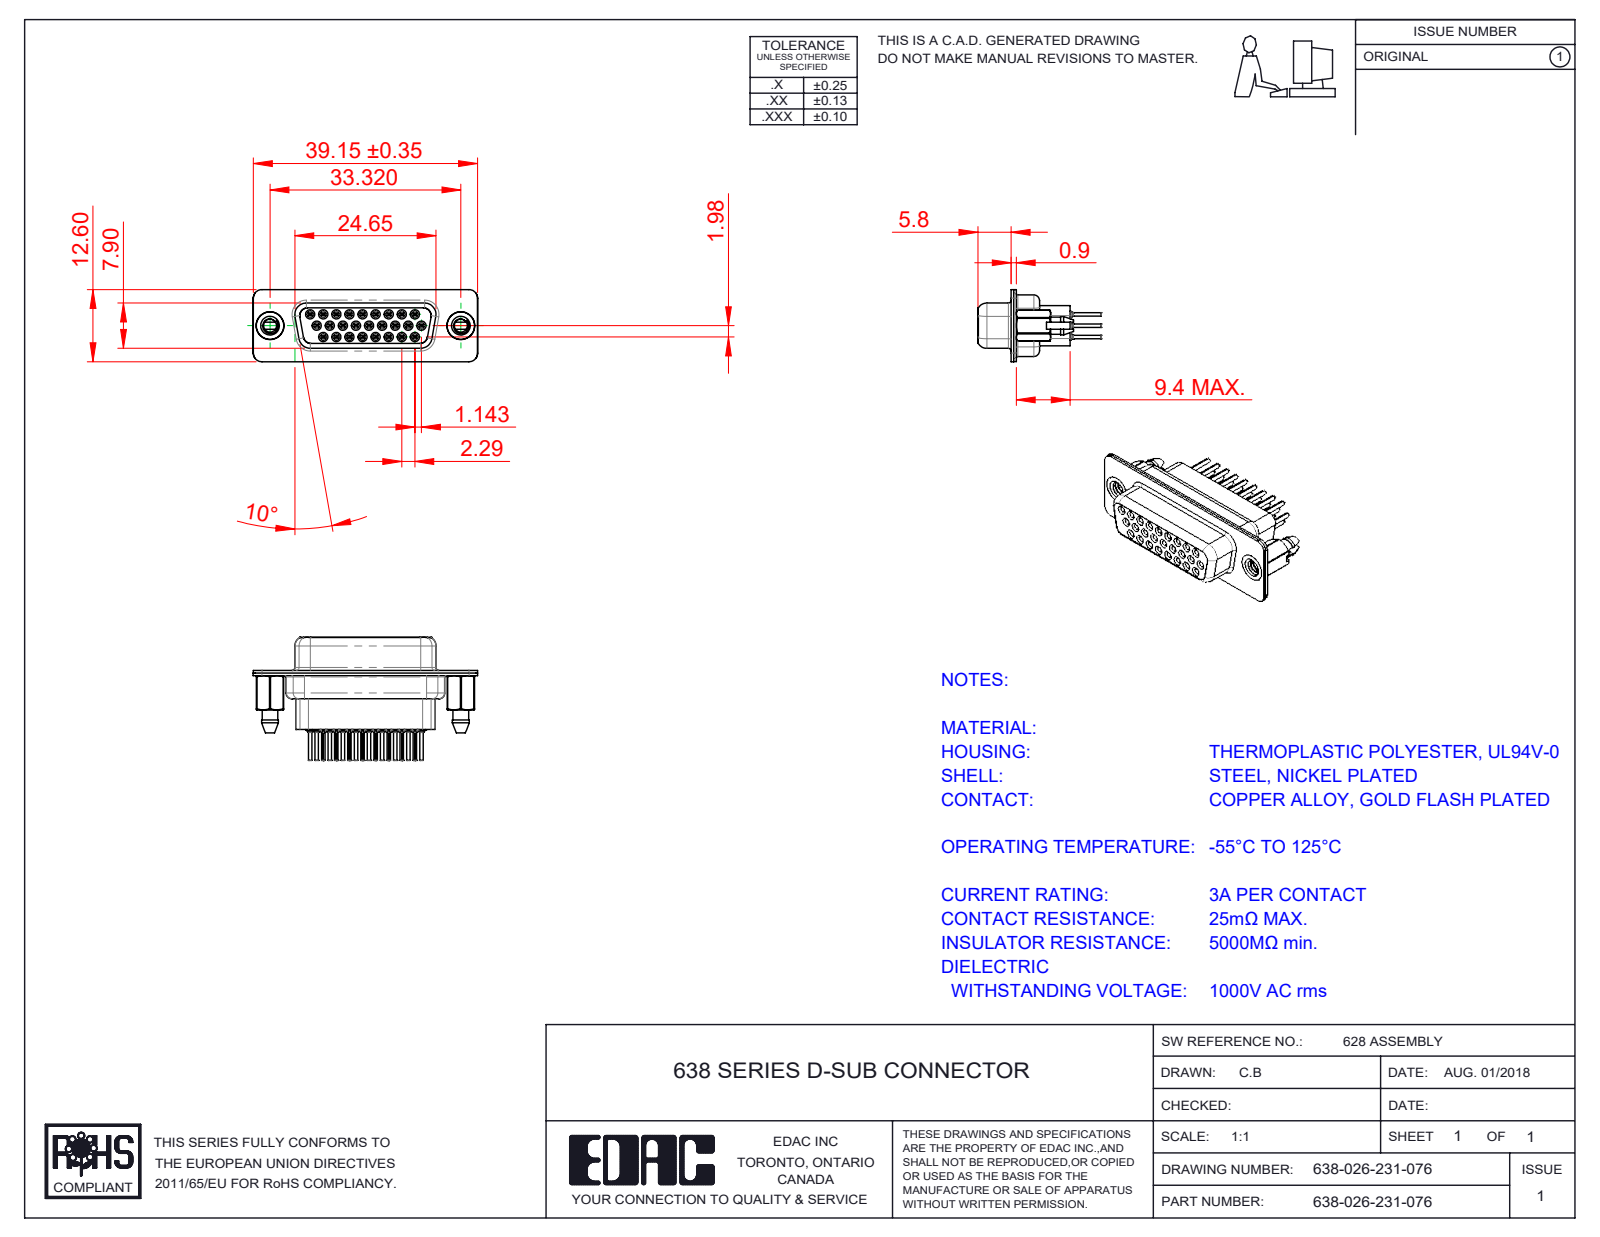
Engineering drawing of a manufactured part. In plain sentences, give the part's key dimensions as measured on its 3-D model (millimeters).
The part is named "638 4-40 Threaded Boardlock_LP; 638 Housing_26 Contacts HP; 638-026-231-076; 638 Shell Front_26 Contacts (+4 more)". Its 3-D file was written by "SolidWorks 2020 (CONFIG_CONTROL_DESIGN)". It is 31 solids with 3551 faces: 905 planar, 1027 cylindrical and 1619 other. Overall it measures 39.19 by 21.5 by 12.6 millimeters. Its volume is 2 790 cubic millimeters and its surface area 10 158 square millimeters. Round holes: 26 of diameter 0.2, 26 of diameter 0.8, 26 of diameter 1, 26 of diameter 1.1, 26 of diameter 1.6, 26 of diameter 1.7, 26 of diameter 1.8, 2 of diameter 2.26, 2 of diameter 4, 2 of diameter 4.05, 2 of diameter 4.85. Round bosses or shafts: 26 of diameter 2, 26 of diameter 1.5, 26 of diameter 1.2, 26 of diameter 0.6, 2 of diameter 4.95, 2 of diameter 4.8. Partial cylindrical surfaces (rounded edges, fillets, slot ends): 52 of radius 0.1, 22 of radius 1.5, 18 of radius 0.28, 12 of radius 2, 8 of radius 1.55, 5 of radius 1.35, 4 of radius 0.25, 4 of radius 0.5. The main face-to-face distances are 0.45, 0.4, 6.6, 1.43, 8.88, 0.9, 7, 2.28, 5.8, 7.05. The hole center spacings are 3.96, 2.28, 4.57, 6.05, 2.29, 8.24, 6.86, 10.48.
